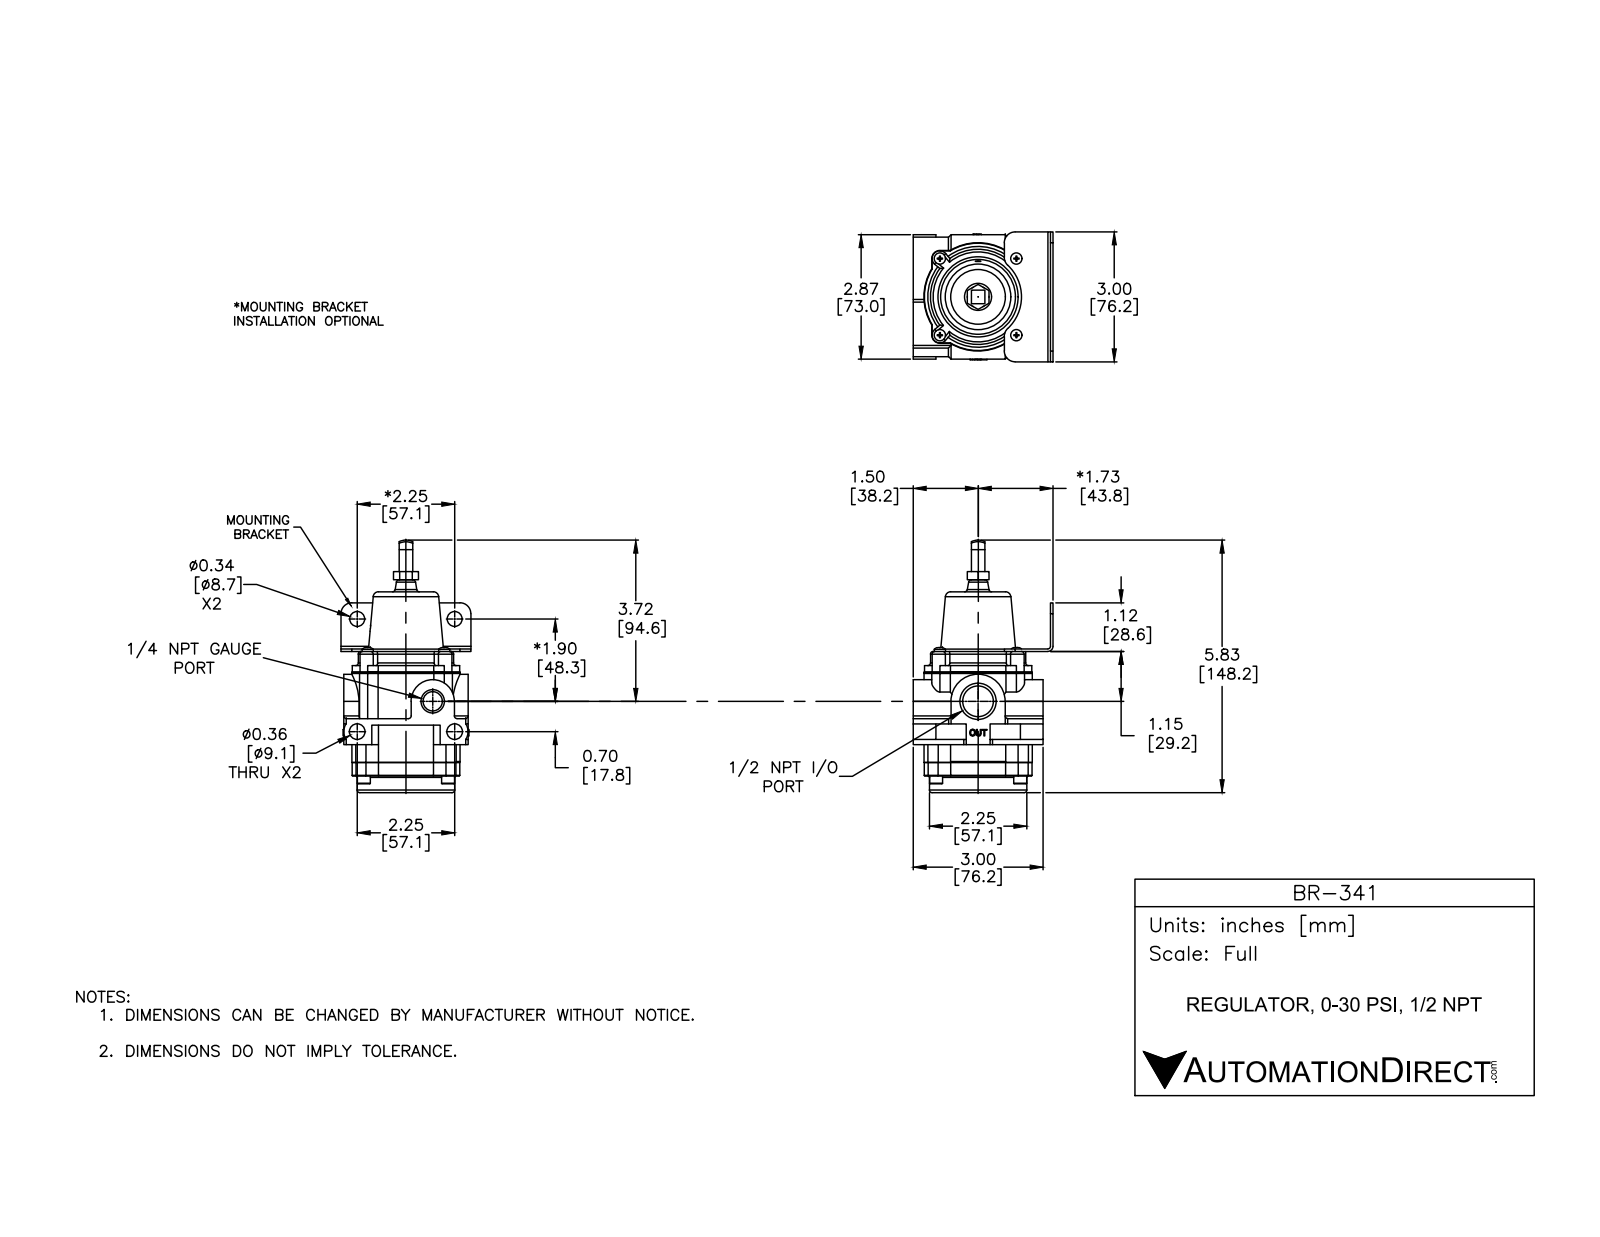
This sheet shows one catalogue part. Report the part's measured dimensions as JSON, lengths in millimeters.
{"part_name": "BR-341", "step_written_by": "SolidWorks 2015 (CONFIG_CONTROL_DESIGN)", "units": "millimeters", "bodies": {"solids": 13, "faces": 1491, "planar": 287, "cylindrical": 973, "other": 231}, "overall_size": [150.8, 76.2, 73.5], "volume_mm3": 330900, "surface_area_mm2": 66710, "round_holes": [[4, 8], [5.1, 4], [5.3, 4], [9.1, 2], [3.2, 1], [6.5, 1], [11.1, 1], [17.9, 1]], "round_bosses_or_shafts": [[4.8, 8], [3.8, 8], [7.9, 5], [9.5, 4], [57.2, 1], [13, 1], [5.2, 1]], "partial_cylinders_radius": [[0.1, 48], [4.8, 12], [0.5, 6], [1.6, 5], [1.6, 5], [4.7, 4], [8, 2], [12.7, 1]], "face_to_face_distances": [52.7, 18.1, 70.8, 28.6, 10.5, 42.2, 30, 30.7, 43.8, 25.8], "hole_center_spacings": [47.2, 3.2, 49.4, 34.9, 31.8, 31.8, 44.9, 44.9]}
